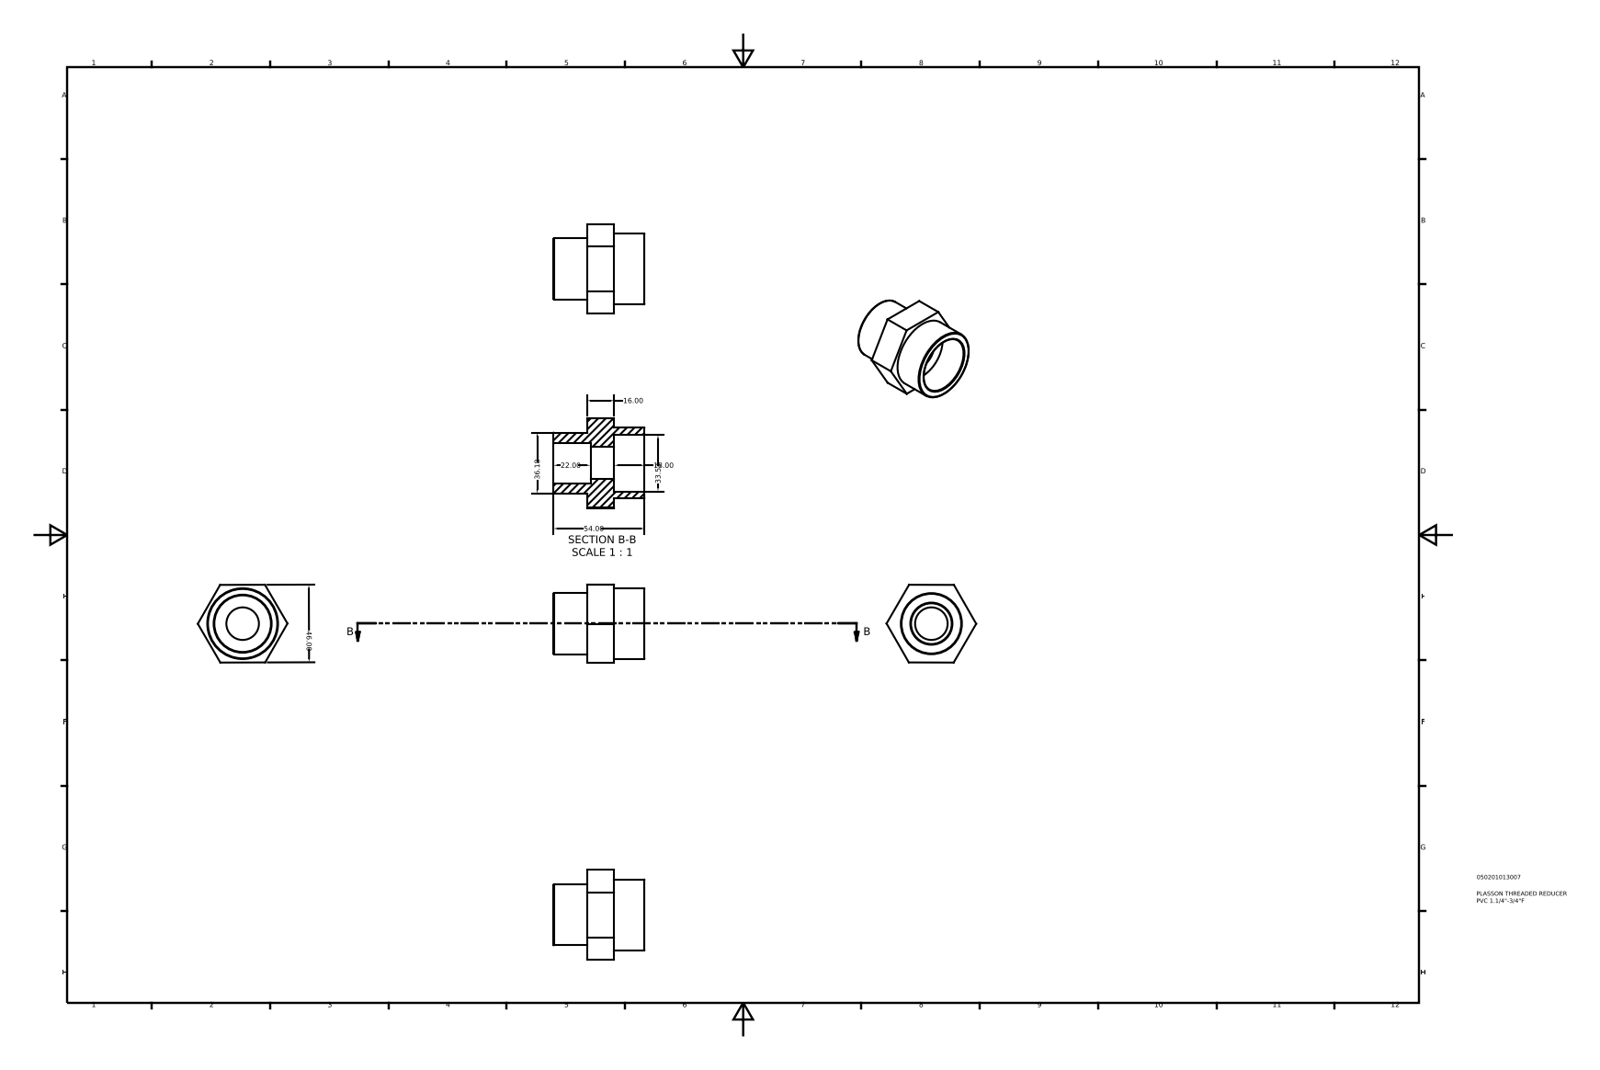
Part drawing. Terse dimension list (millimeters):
name: 050201013007
written by: Autodesk Inventor 2015 (AUTOMOTIVE_DESIGN)
unit: mm
bodies: 1 solid, 21 faces (12 planar, 5 cylindrical, 4 other)
size: 54 × 53.12 × 46.08
volume: 44 657 mm³; area: 14 607 mm²
holes: 1× ⌀19.29, 1× ⌀24.12, 1× ⌀33.53
bosses: 1× ⌀41.91, 1× ⌀36.18
face distances: 16, 20, 36, 46.02, 46, 46.04, 54, 34, 18, 22
